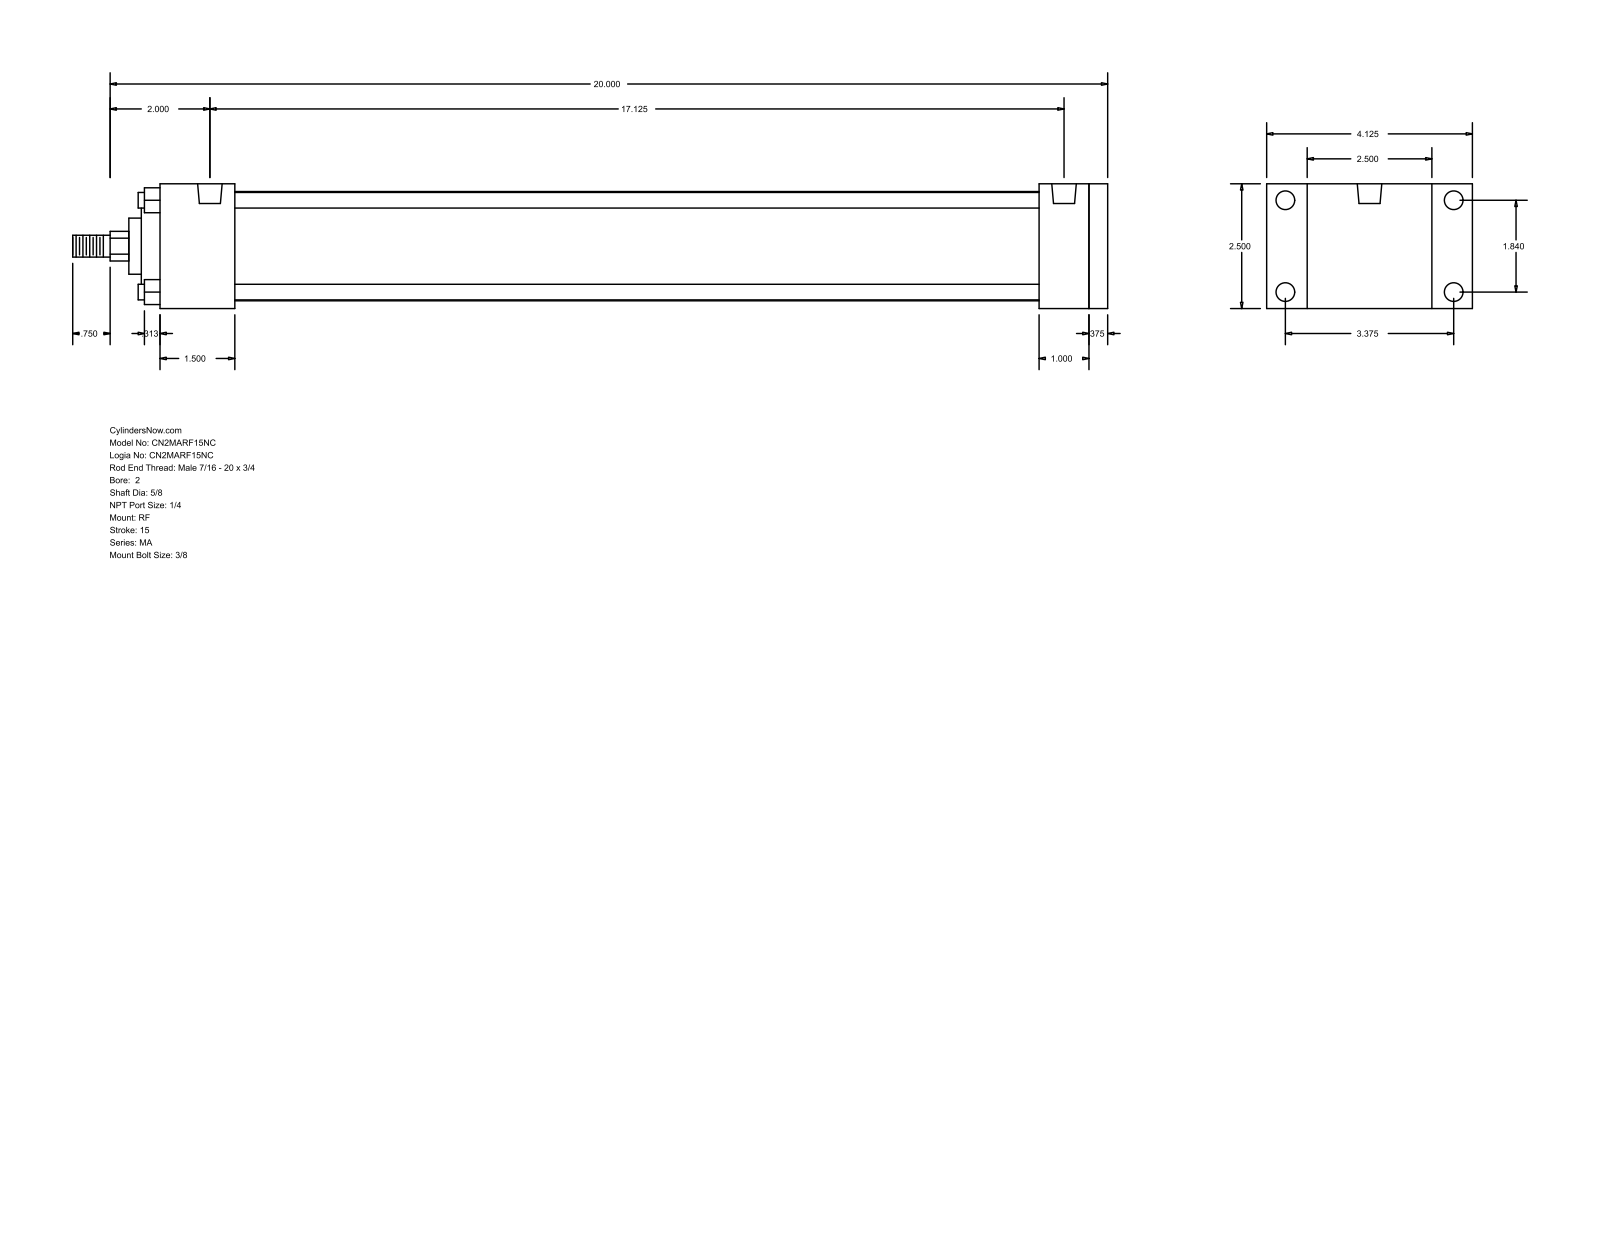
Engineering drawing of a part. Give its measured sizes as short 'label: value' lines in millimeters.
name: MA_RF__0200_0.625
written by: GSSL Pune (CONFIG_CONTROL_DESIGN)
unit: mm
bodies: 0 solids, 94 faces (65 planar, 29 cylindrical, 0 other)
size: 527.05 × 104.78 × 63.5
holes: 4× ⌀7.94, 4× ⌀9.53, 2× ⌀12.49
bosses: 4× ⌀7.94, 1× ⌀55.63, 1× ⌀50.8, 1× ⌀28.57, 1× ⌀15.88, 1× ⌀11.11
rounds: 1× R7.54
face distances: 63.5, 9.52, 482.6, 38.1, 34.93, 492.12, 473.08, 434.98, 444.5, 447.67
hole spacings: 46.74, 85.72, 97.63, 434.97
